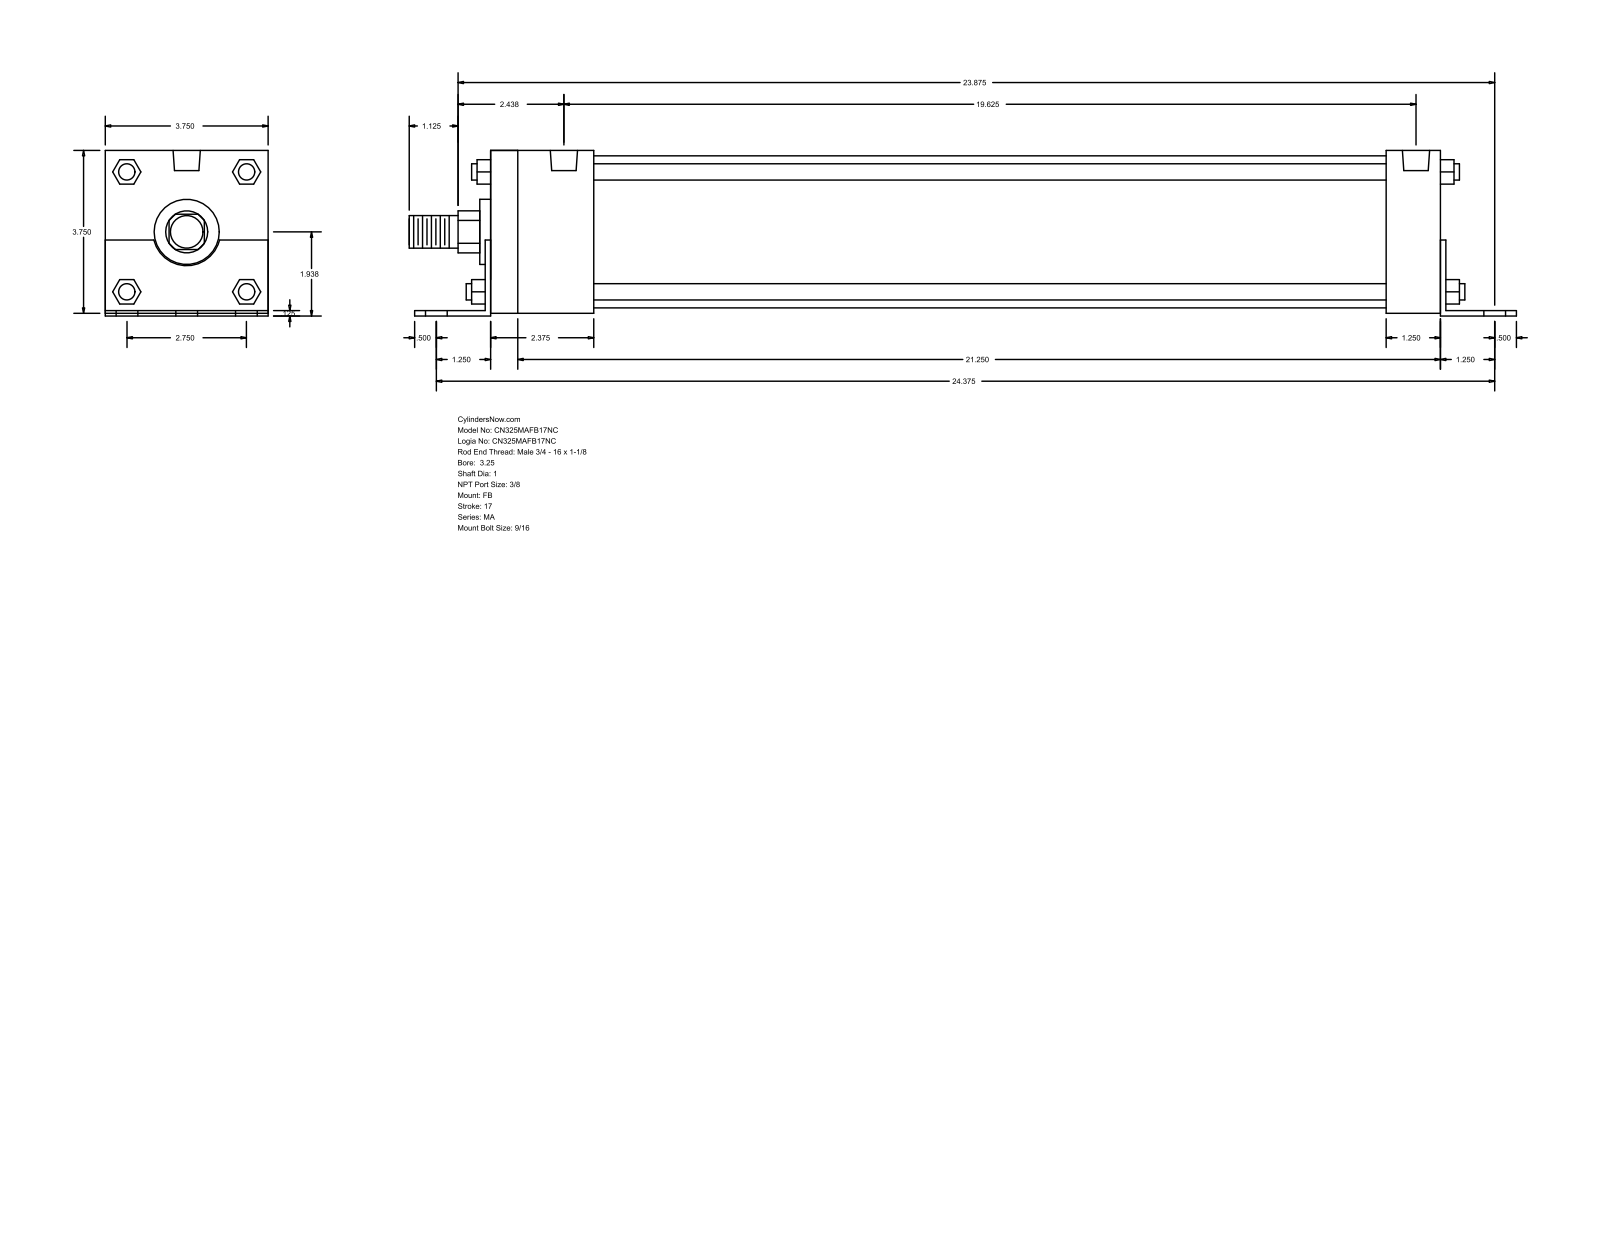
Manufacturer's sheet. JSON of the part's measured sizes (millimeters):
{"part_name": "MA_FB__0325_1", "step_written_by": "GSSL Pune (CONFIG_CONTROL_DESIGN)", "units": "millimeters", "bodies": {"solids": 0, "faces": 140, "planar": 105, "cylindrical": 35, "other": 0}, "overall_size": [647.7, 96.84, 95.25], "round_holes": [[14.29, 6], [11.11, 4], [15.93, 2]], "round_bosses_or_shafts": [[9.53, 4], [88.9, 1], [38.1, 1], [25.4, 1], [19.05, 1]], "partial_cylinders_radius": [[12.29, 1], [19.81, 1]], "face_to_face_distances": [95.24, 3.17, 1.59, 96.83, 1.58, 93.66, 3.18, 555.62, 561.97, 558.8], "hole_center_spacings": [34.92, 620.1, 619.12, 57.78, 61.64, 69.84, 82.38, 86.71]}
